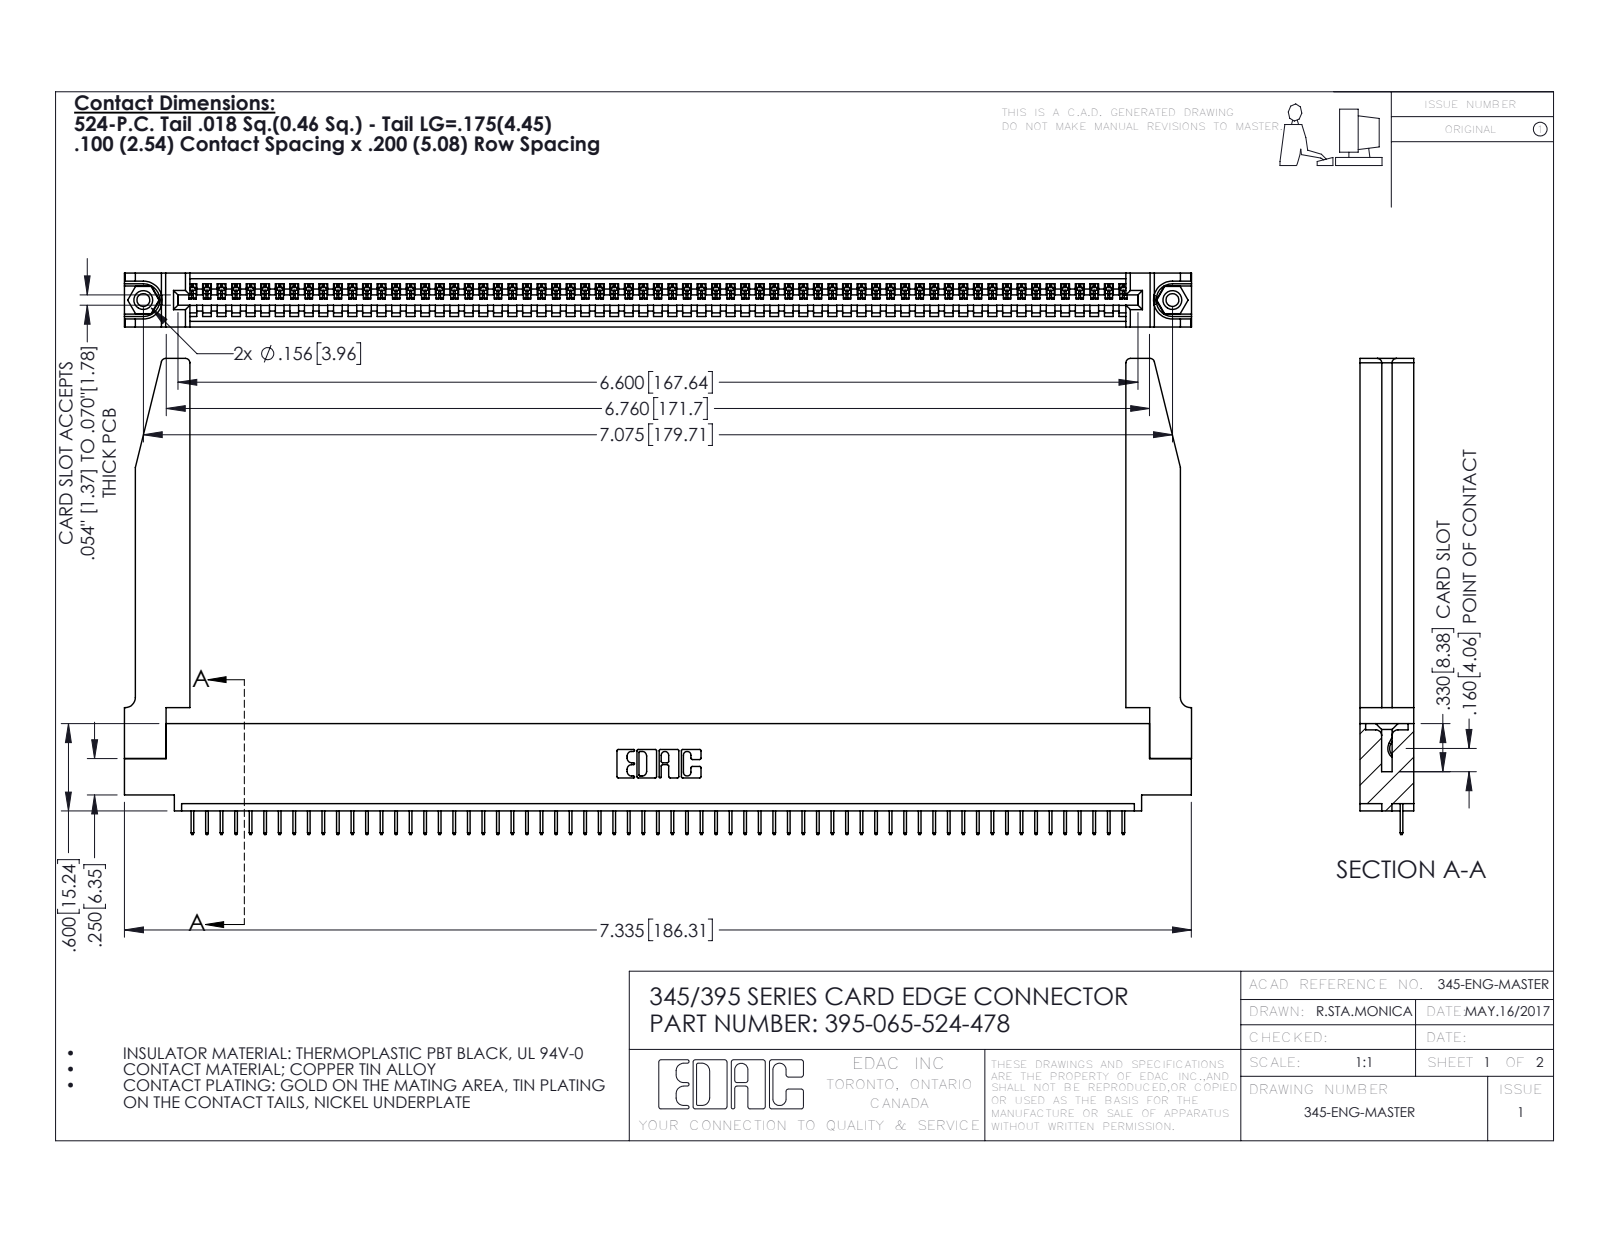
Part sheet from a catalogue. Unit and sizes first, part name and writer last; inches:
Units: inches
Overall size (bounding box): 7.336 × 3.272 × 0.37
Round holes (diameter × count): ⌀0.089 ×2, ⌀0.125 ×2, ⌀0.156 ×2, ⌀0.064 ×1
Round bosses / shafts (diameter × count): ⌀0.155 ×2
Partial cylindrical surfaces — rounded edges, fillets, slot ends (radius × count): R0.006 ×130, R0.01 ×22, R0.03 ×8, R0.007 ×6, R0.031 ×6, R0.026 ×3, R0.031 ×2, R0.04 ×2
Main face-to-face distances: 0.37, 0.072, 0.298, 0.2, 0.098, 0.272, 0.025, 0.225, 0.072, 0.148
Hole centre spacings: 0.27, 6.839, 7.075
Volume: 1.546 in³ · Surface area: 46.11 in²
Bodies: 70 solids, 4394 faces (3216 planar, 1126 cylindrical, 52 other)
Part name (STEP PRODUCT): 345-292-001_345-293-124; 345-220-078_345-220-078; 345-250-001_345-250-001-102; 345 Part_0.110 Offset - 0.156 Dia-TH (+1 more)
STEP written by: SolidWorks 2016 (CONFIG_CONTROL_DESIGN)
